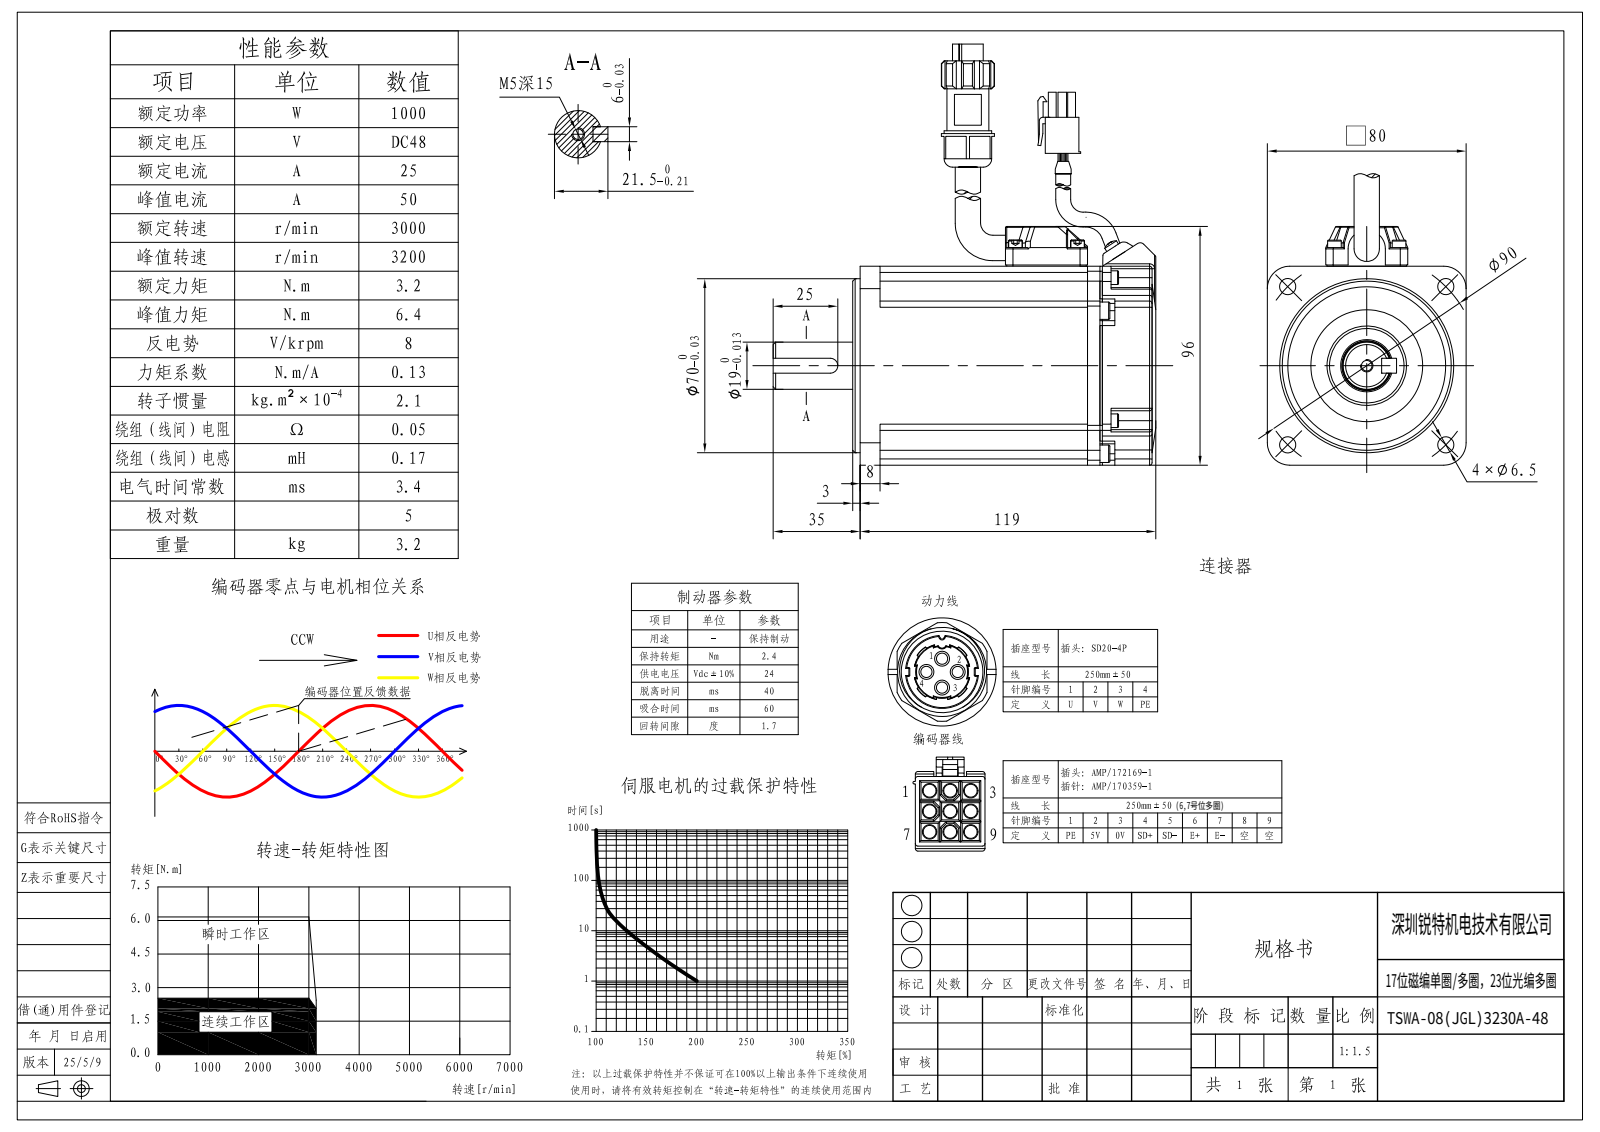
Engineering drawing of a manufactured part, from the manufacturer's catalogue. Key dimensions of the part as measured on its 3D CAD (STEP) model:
STEP written by: SolidWorks 2018 (CONFIG_CONTROL_DESIGN)
Units: millimetres
Bodies: 30 solids, 1609 faces (514 planar, 524 cylindrical, 571 other)
Overall size (bounding box): 157.5 × 92.5 × 80
Volume: 263 723 mm³ · Surface area: 158 365 mm²
Round holes (diameter × count): ⌀3.3 ×14, ⌀3.2 ×8, ⌀2.5 ×7, ⌀4.2 ×5, ⌀3.5 ×4, ⌀4.5 ×4, ⌀6.5 ×4, ⌀2 ×2, ⌀6 ×1, ⌀6.3 ×1, ⌀7.6 ×1, ⌀8 ×1
Round bosses / shafts (diameter × count): ⌀4 ×10, ⌀7 ×8, ⌀5.5 ×6, ⌀3 ×6, ⌀11.6 ×2, ⌀2.2 ×2, ⌀2 ×2, ⌀74.7 ×1
Partial cylindrical surfaces — rounded edges, fillets, slot ends (radius × count): R1 ×57, R0.5 ×25, R2 ×21, R8 ×12, R0.6 ×9, R2.5 ×8, R4 ×8, R3 ×5
Main face-to-face distances: 80, 2.5, 0.5, 14, 1.5, 66, 1, 5.5, 3, 5
Hole centre spacings: 58.87, 8, 10.39, 18.73, 41.5, 53.92, 70.6, 83.25
